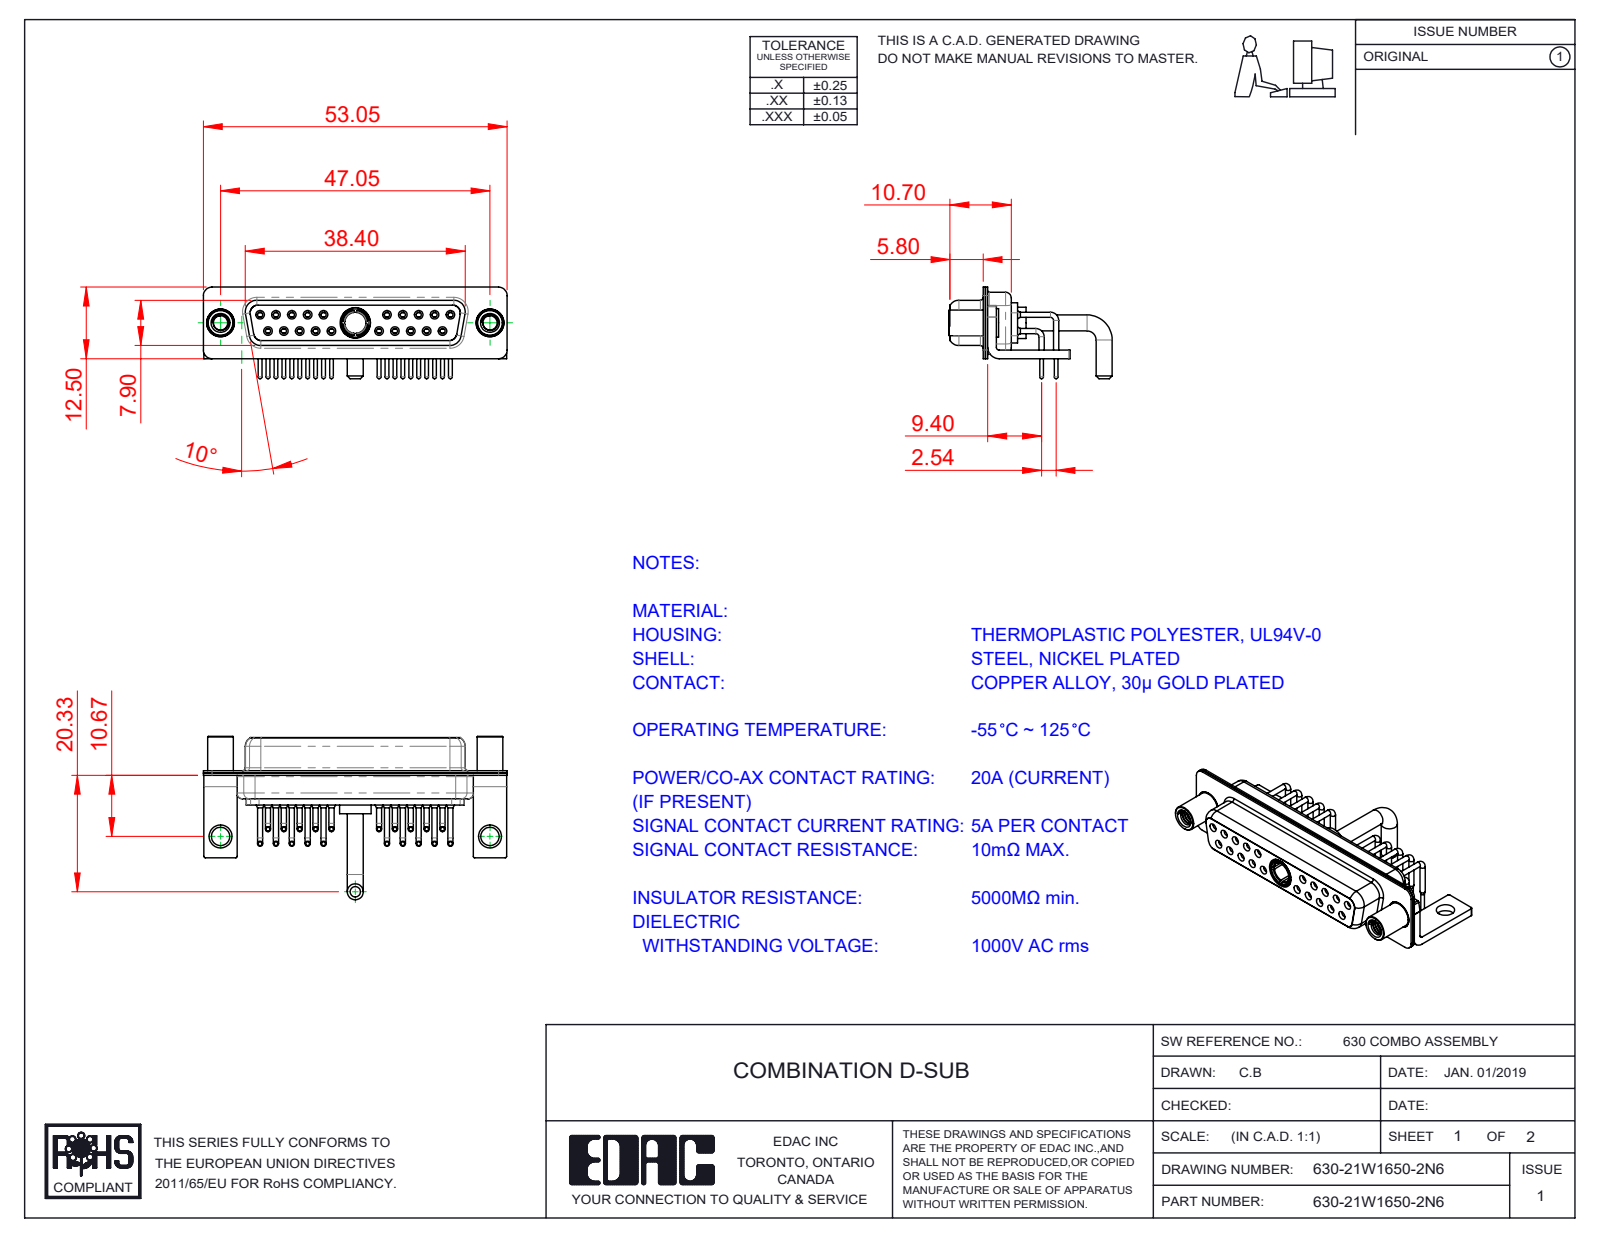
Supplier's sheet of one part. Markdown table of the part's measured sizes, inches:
| quantity | value |
| --- | --- |
| part name | 630-21W1650-2N6; 630Combo Shell Rear_25 Contacts; 630Combo Shell Front_25 Contacts; Power Socket_Ext 20A RA (+5 more) |
| STEP written by | SolidWorks 2020 (CONFIG_CONTROL_DESIGN) |
| units | inches |
| bodies | 29 solids, 1515 faces (418 planar, 694 cylindrical, 403 other) |
| overall size | 2.089 × 1.123 × 0.63 |
| volume | 0.272 in³ |
| surface area | 16.02 in² |
| round holes (diameter × count) | 0.035 × 20, 0.043 × 20, 0.059 × 20, 0.079 × 20, 0.063 × 10, 0.067 × 10, 0.191 × 3, 0.098 × 2, 0.126 × 2, 0.157 × 2, 0.159 × 2, 0.146 × 1 |
| round bosses / shafts (diameter × count) | 0.035 × 20, 0.026 × 20, 0.063 × 10, 0.197 × 2, 0.195 × 2, 0.189 × 2, 0.177 × 2, 0.11 × 2 |
| partial cylindrical surfaces (radius × count) | 0.01 × 16, 0.059 × 16, 0.079 × 13, 0.053 × 8, 0.063 × 8, 0.02 × 5, 0.024 × 4, 0.026 × 4 |
| main face-to-face distances | 0.016, 0.018, 0.055, 0.333, 0.031, 0.071, 0.35, 0.244, 0.278, 0.059 |
| hole center spacings | 0.124, 0.109, 0.218, 0.327, 0.198, 0.763, 0.826, 0.872 |
